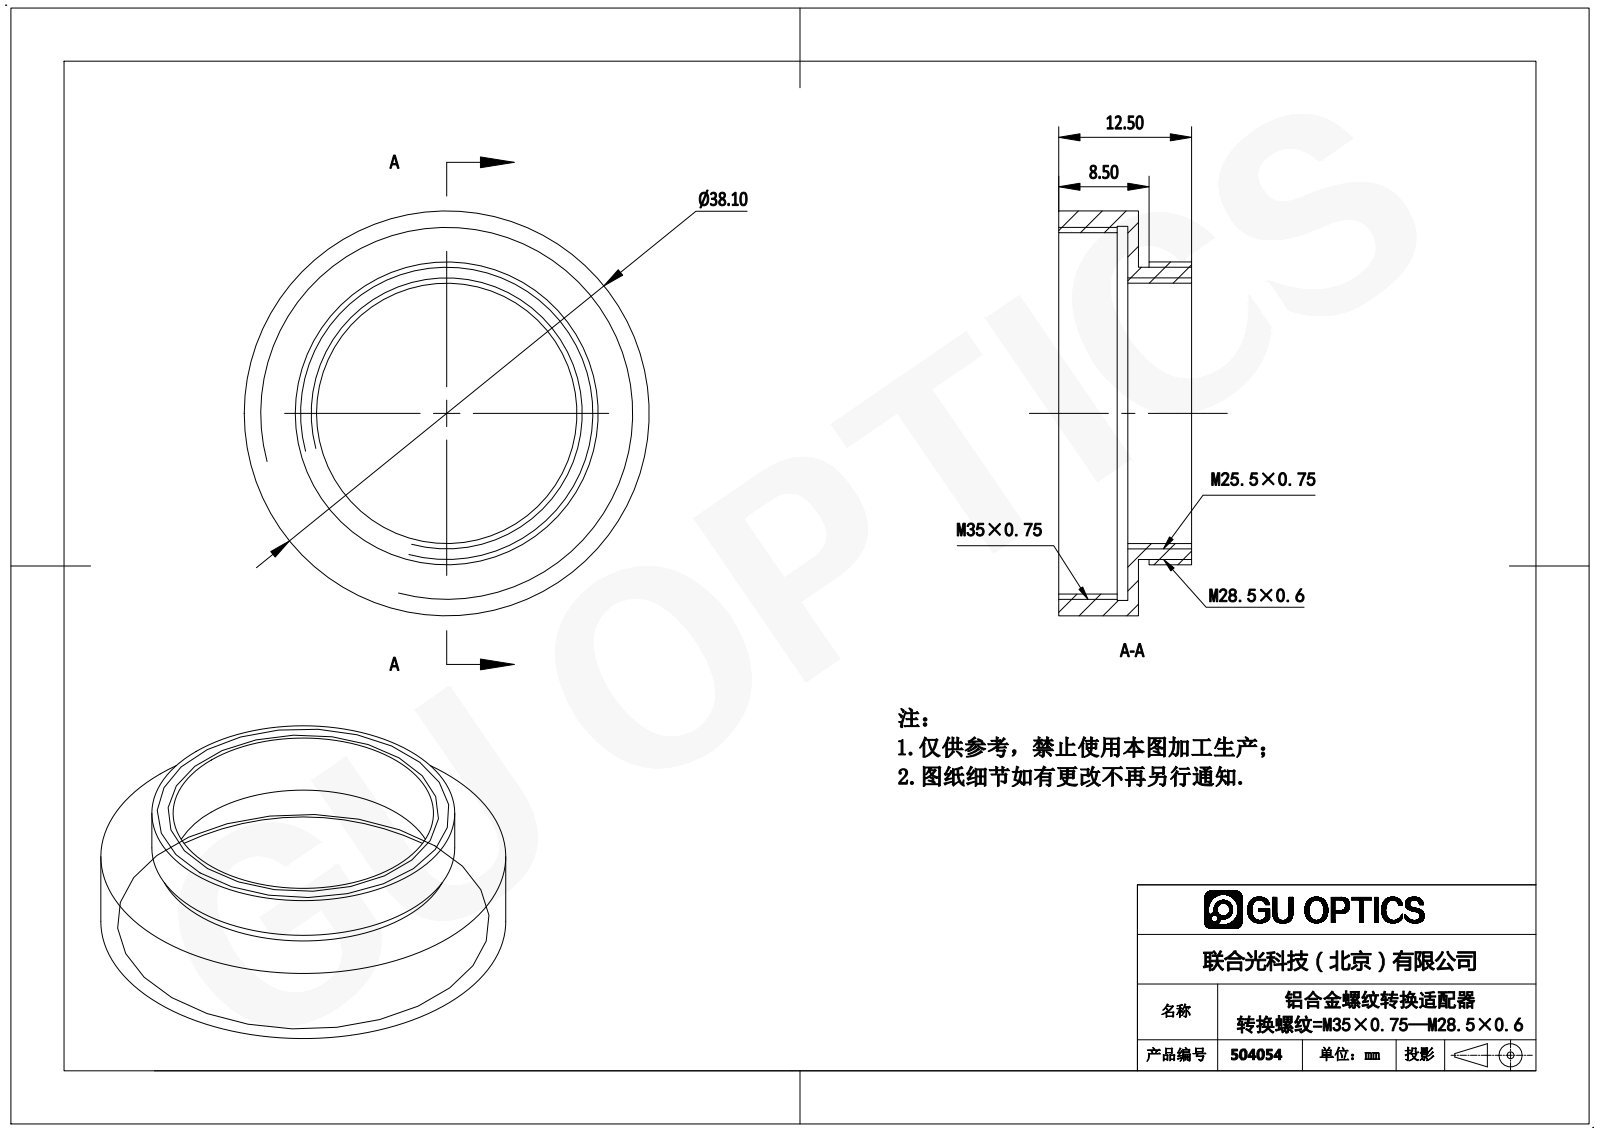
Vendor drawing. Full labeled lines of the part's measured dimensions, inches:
Part name (STEP PRODUCT): 504054
STEP written by: SolidWorks 2016 (AUTOMOTIVE_DESIGN)
Units: inches
Bodies: 1 solid, 18 faces (6 planar, 12 cylindrical, 0 other)
Overall size (bounding box): 1.5 × 1.5 × 0.492
Volume: 0.177 in³ · Surface area: 6.29 in²
Round holes (diameter × count): ⌀0.965 ×1, ⌀1.339 ×1, ⌀1.386 ×1
Round bosses / shafts (diameter × count): ⌀1.5 ×1, ⌀1.122 ×1, ⌀1.083 ×1
Main face-to-face distances: 0.039, 0.256, 0.295, 0.492, 0.236, 0.197, 0.079, 0.217, 0.276, 0.335
